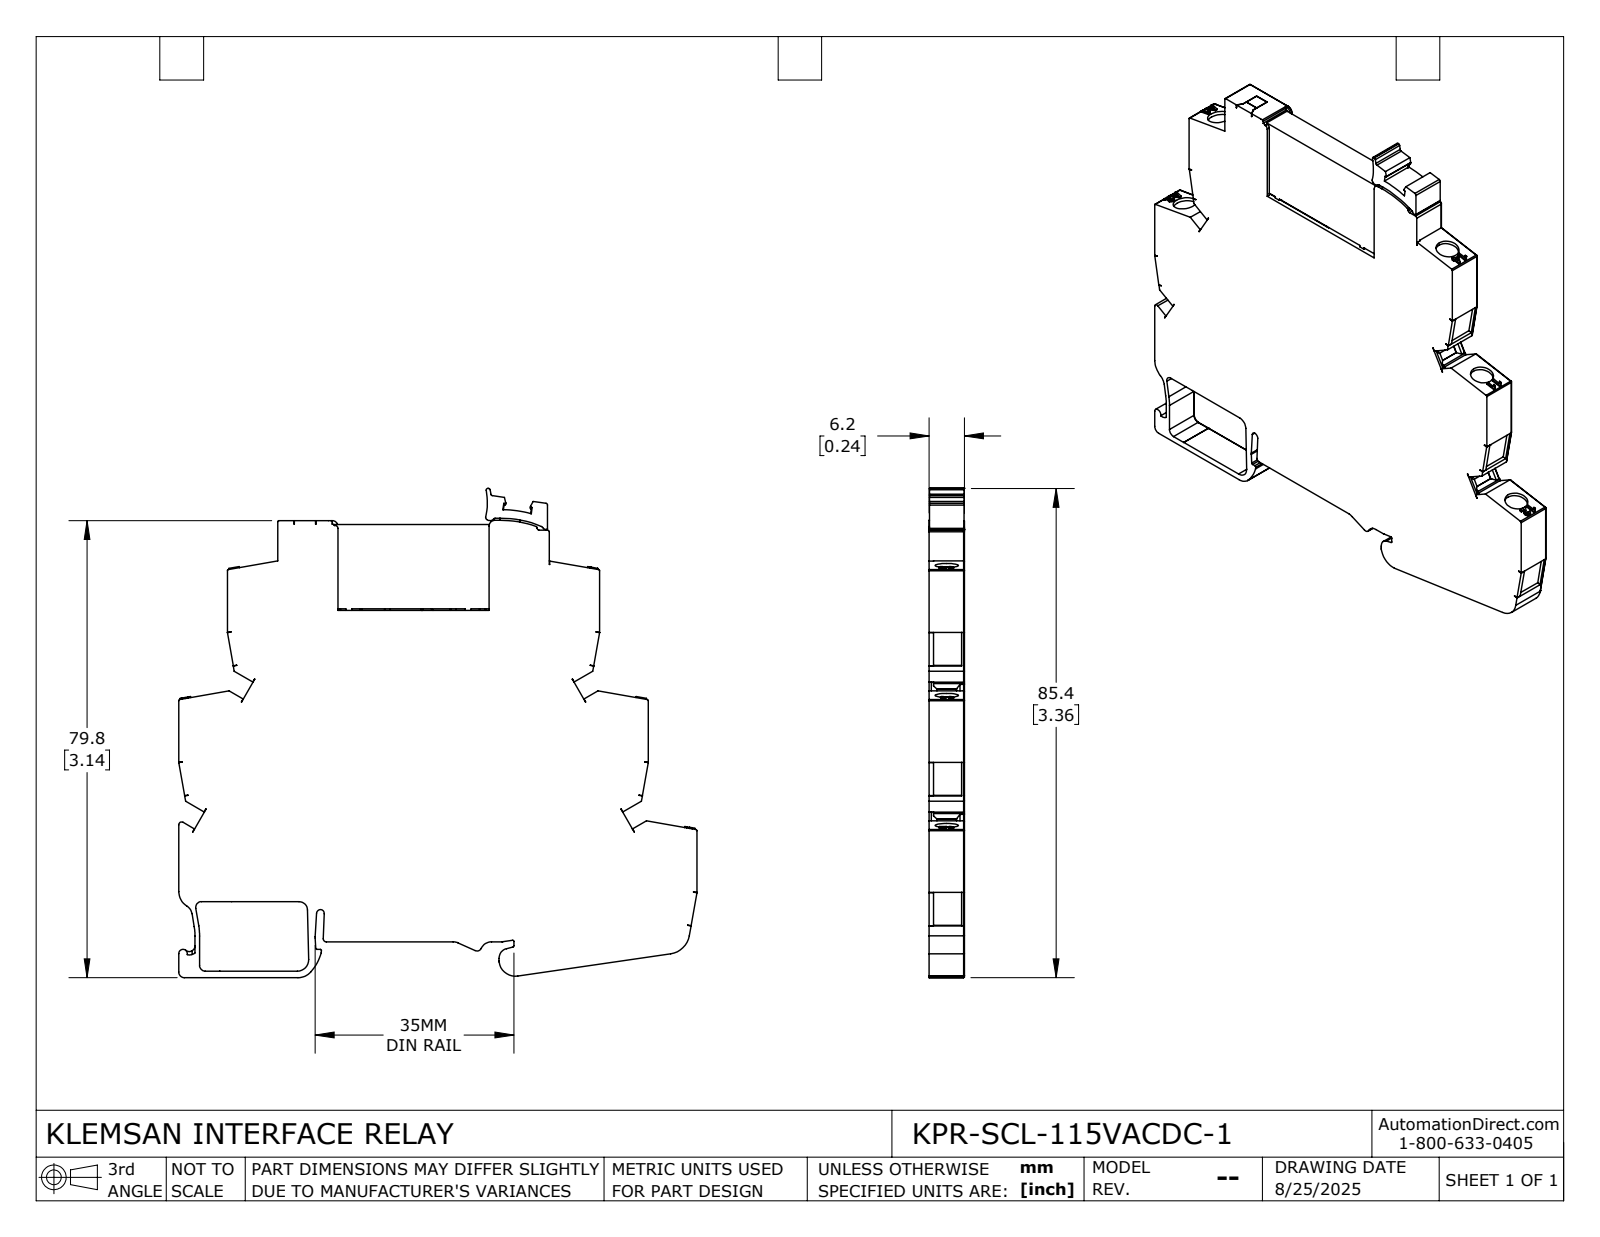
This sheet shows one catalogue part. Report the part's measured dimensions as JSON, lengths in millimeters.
{"part_name": "KPR-SCL-115VACDC-1", "step_written_by": "SolidWorks 2024 (CONFIG_CONTROL_DESIGN)", "units": "millimeters", "bodies": {"solids": 1, "faces": 764, "planar": 578, "cylindrical": 148, "other": 38}, "overall_size": [90.49, 85.41, 6.2], "volume_mm3": 33364, "surface_area_mm2": 14579, "round_holes": [[4.05, 5]], "round_bosses_or_shafts": [[0.4, 2]], "partial_cylinders_radius": [[0.2, 22], [0.3, 11], [0.1, 10], [1, 9], [0.5, 7], [0.4, 5], [0.9, 5], [2, 5]], "face_to_face_distances": [6.2, 0.6, 5.6, 5, 0.5, 72.82, 58.12, 14.7, 8.49, 8.5], "hole_center_spacings": [12.3, 12.32, 12.33, 24.61]}
